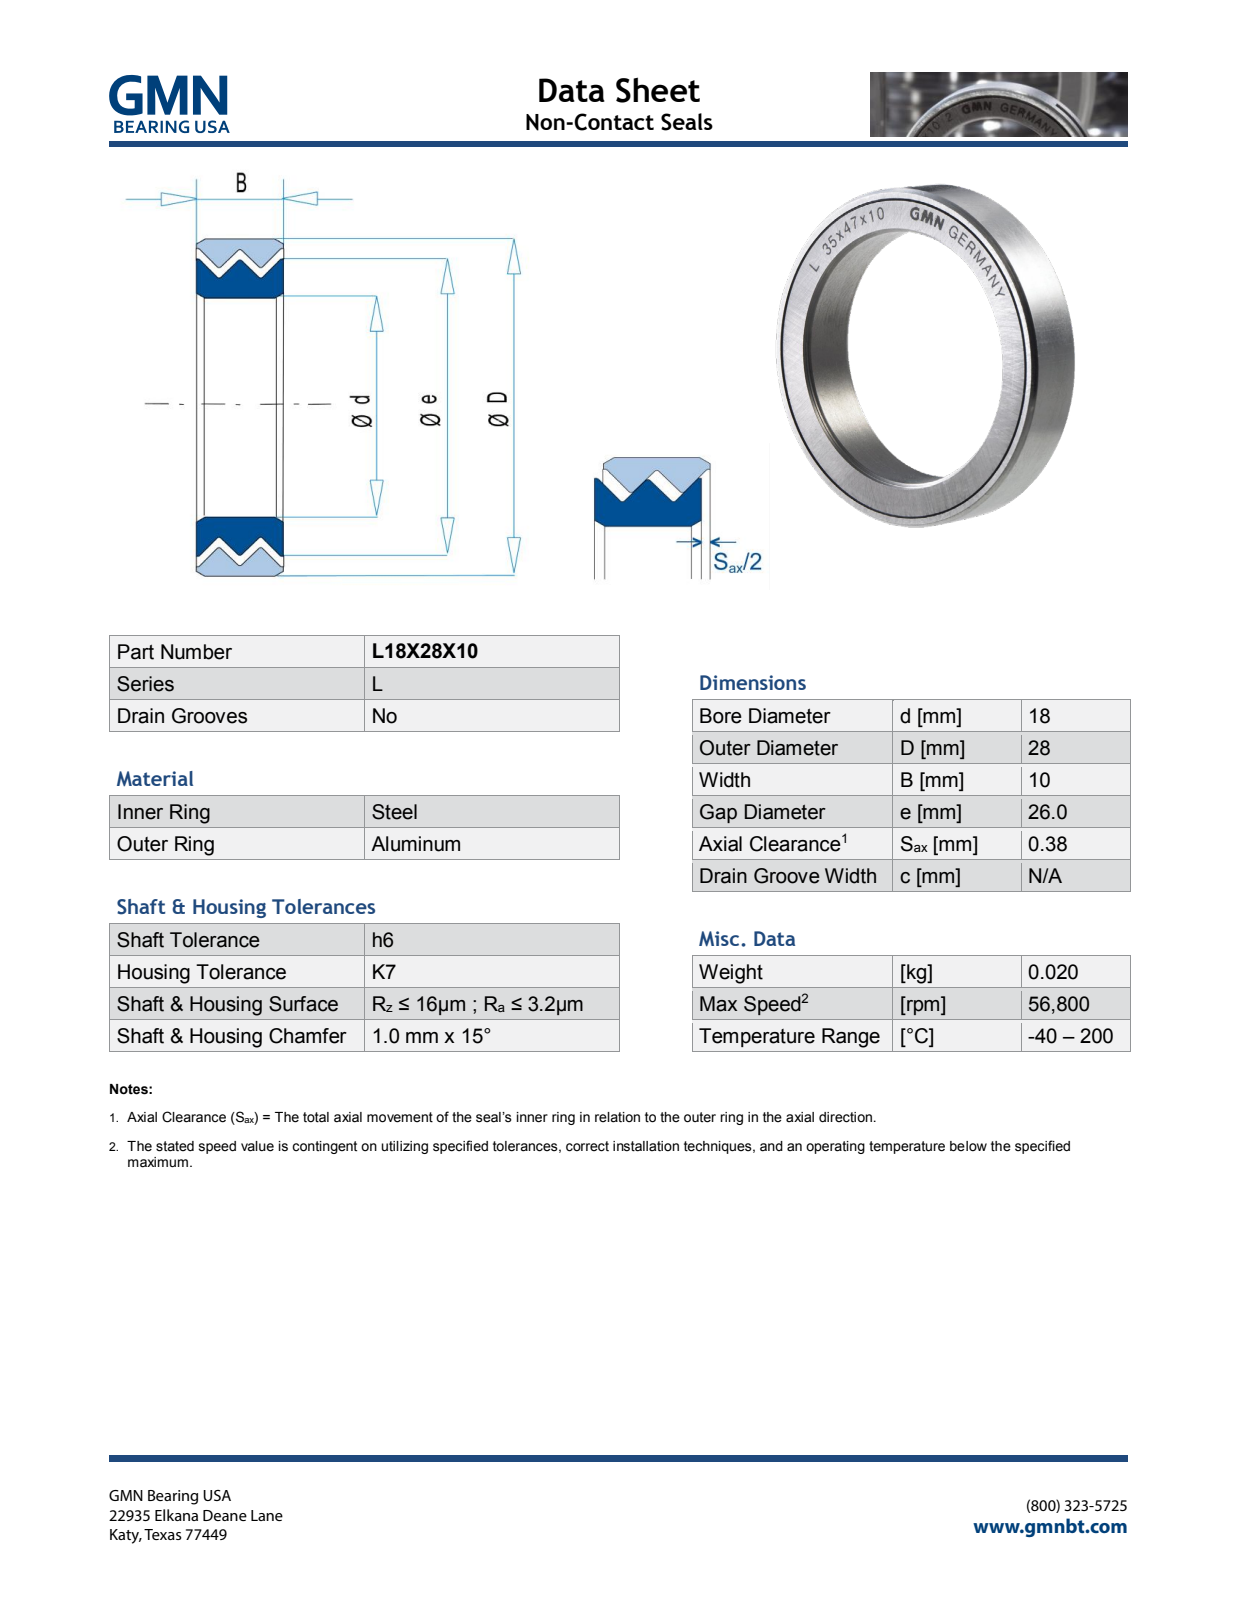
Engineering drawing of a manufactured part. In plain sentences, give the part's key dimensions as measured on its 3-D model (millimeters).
The part is named "L18X28X10_PRT". Its 3-D file was written by "PRO/ENGINEER BY PARAMETRIC TECHNOLOGY CORPORATION, 2013150 (AUTOMOTIVE_DESIGN)". It is 2 solids with 596 faces: 540 planar, 12 cylindrical and 44 other. Overall it measures 28 by 28 by 10.07 millimeters. Its volume is 3 395 cubic millimeters and its surface area 4 049 square millimeters. Round holes: 1 of diameter 18, 1 of diameter 26.27. Round bosses or shafts: 1 of diameter 28, 1 of diameter 26. The main face-to-face distances are 10, 10.07, 1.42, 1.24, 1.25, 1.01, 1.07, 1.06, 0.64, 0.6.
